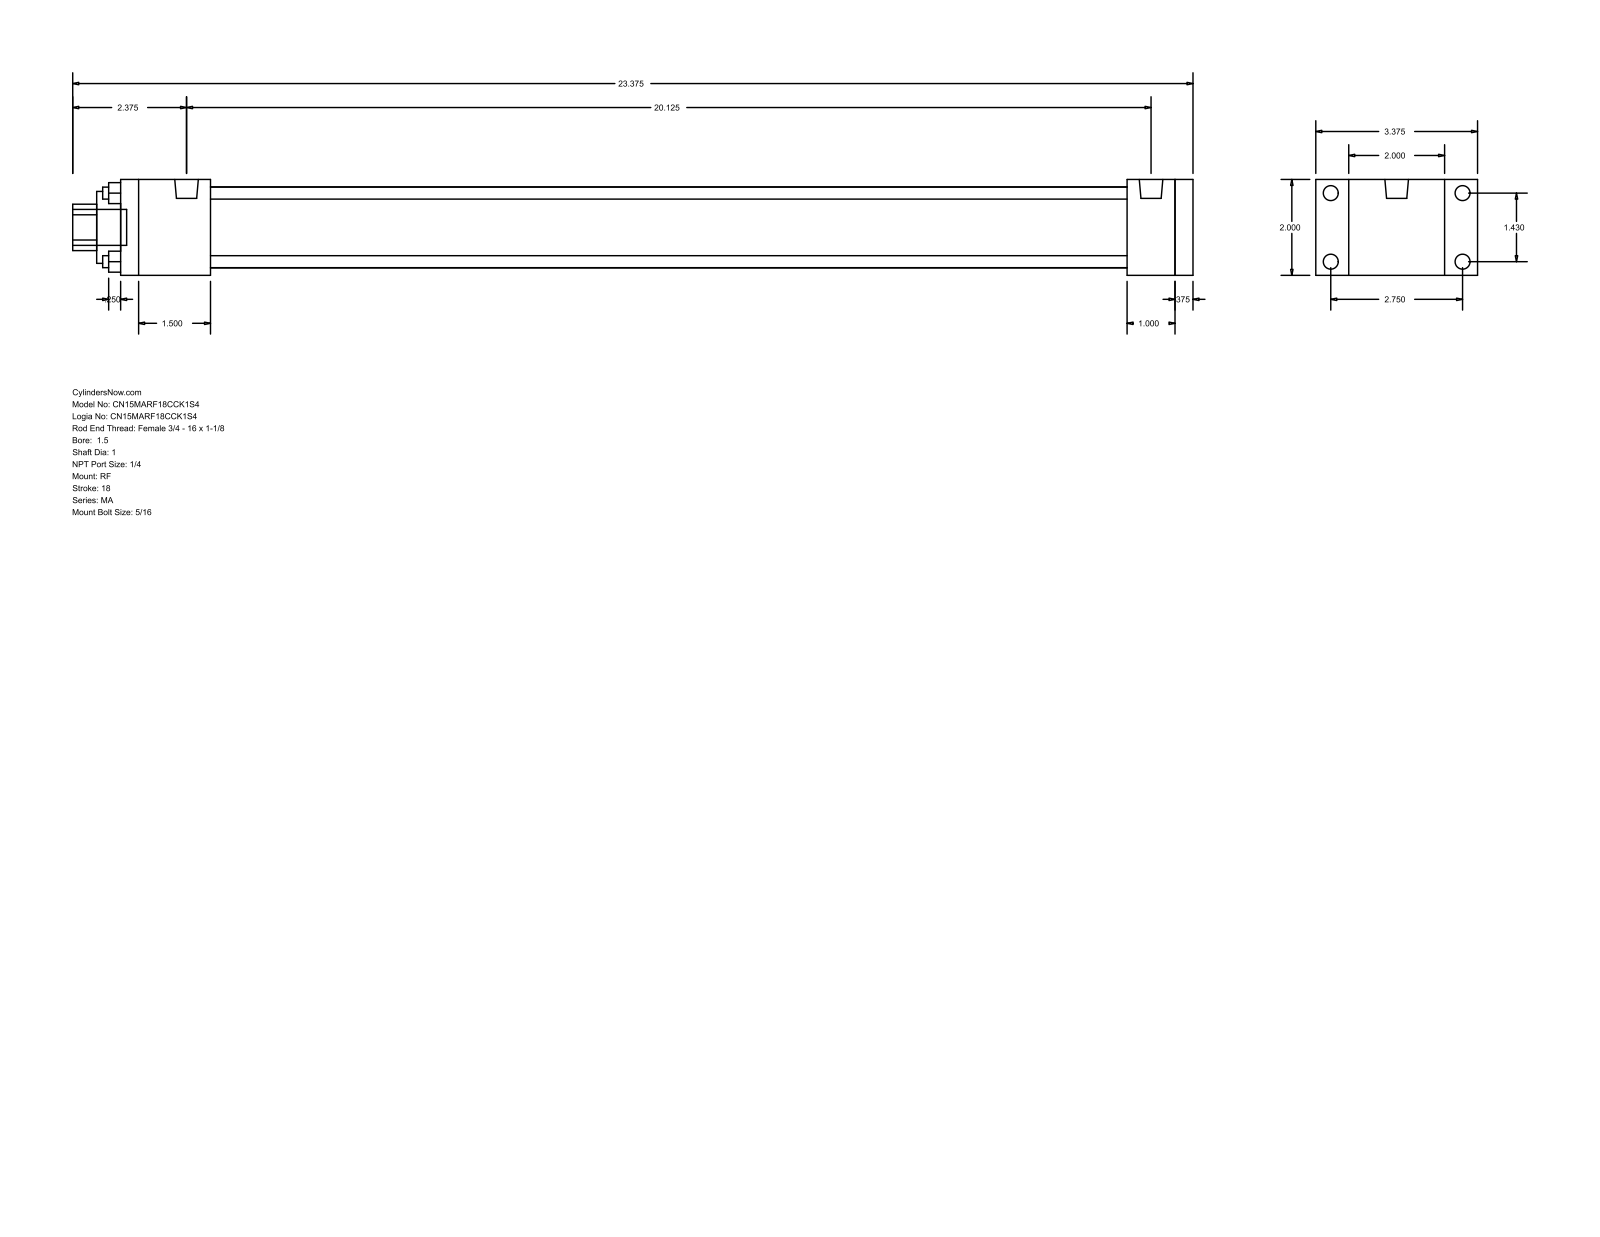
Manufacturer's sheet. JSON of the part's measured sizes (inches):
{"part_name": "MA_RF__0150_1", "step_written_by": "GSSL Pune (CONFIG_CONTROL_DESIGN)", "units": "inches", "bodies": {"solids": 0, "faces": 92, "planar": 64, "cylindrical": 28, "other": 0}, "overall_size": [23.375, 3.375, 2], "round_holes": [[0.25, 4], [1, 1], [1.5, 1], [1.69, 1]], "round_bosses_or_shafts": [[0.313, 8], [0.492, 2], [0.75, 1]], "partial_cylinders_radius": [[0.484, 1]], "face_to_face_distances": [2, 0.375, 22, 1, 22.375, 21, 1.375, 1.875, 19.125, 20.125], "hole_center_spacings": [1.011, 1.43, 2.022]}
